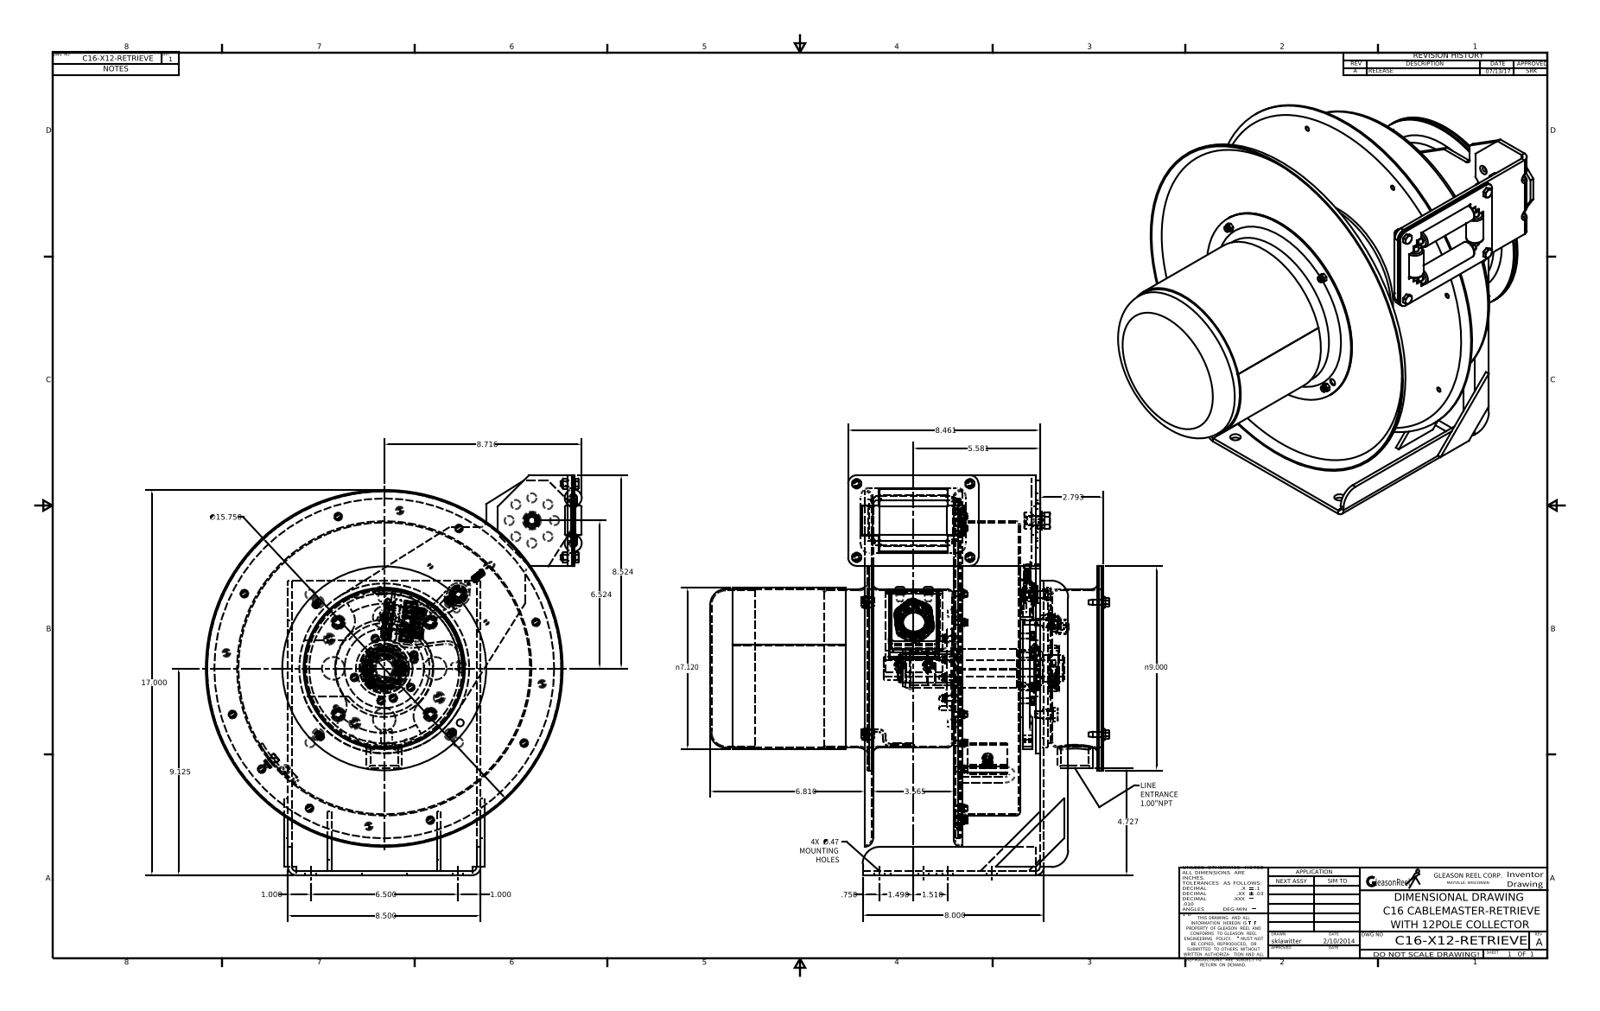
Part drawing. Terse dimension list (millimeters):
name: C16-X12-RETRIEVE (SW)
written by: Autodesk Inventor 2016 (AUTOMOTIVE_DESIGN)
unit: mm
bodies: 160 solids, 3264 faces (1283 planar, 1024 cylindrical, 957 other)
size: 448.28 × 447.17 × 421.41
volume: 3 218 000 mm³; area: 2 713 000 mm²
holes: 28× ⌀6.35, 26× ⌀5, 22× ⌀4.13, 13× ⌀10.31, 12× ⌀5.56, 8× ⌀5.41, 8× ⌀10.67, 8× ⌀11.94, 7× ⌀7.14, 5× ⌀4.92, 5× ⌀25.4, 4× ⌀2.32
bosses: 26× ⌀5, 13× ⌀6.8, 10× ⌀6, 5× ⌀12.7, 5× ⌀11.6, 5× ⌀8.9, 5× ⌀8, 4× ⌀19.05
rounds: 67× R0.76, 64× R0.24, 57× R0.38, 18× R1.98, 12× R0.15, 12× R1.52, 8× R3.15, 8× R6.35
face distances: 1.52, 4.55, 3.17, 165.02, 4.7, 96.75, 98.28, 1.53, 1.5, 6.2
hole spacings: 103.2, 44.43, 103.25, 145.95, 190.49, 138.31, 19.44, 44.54
